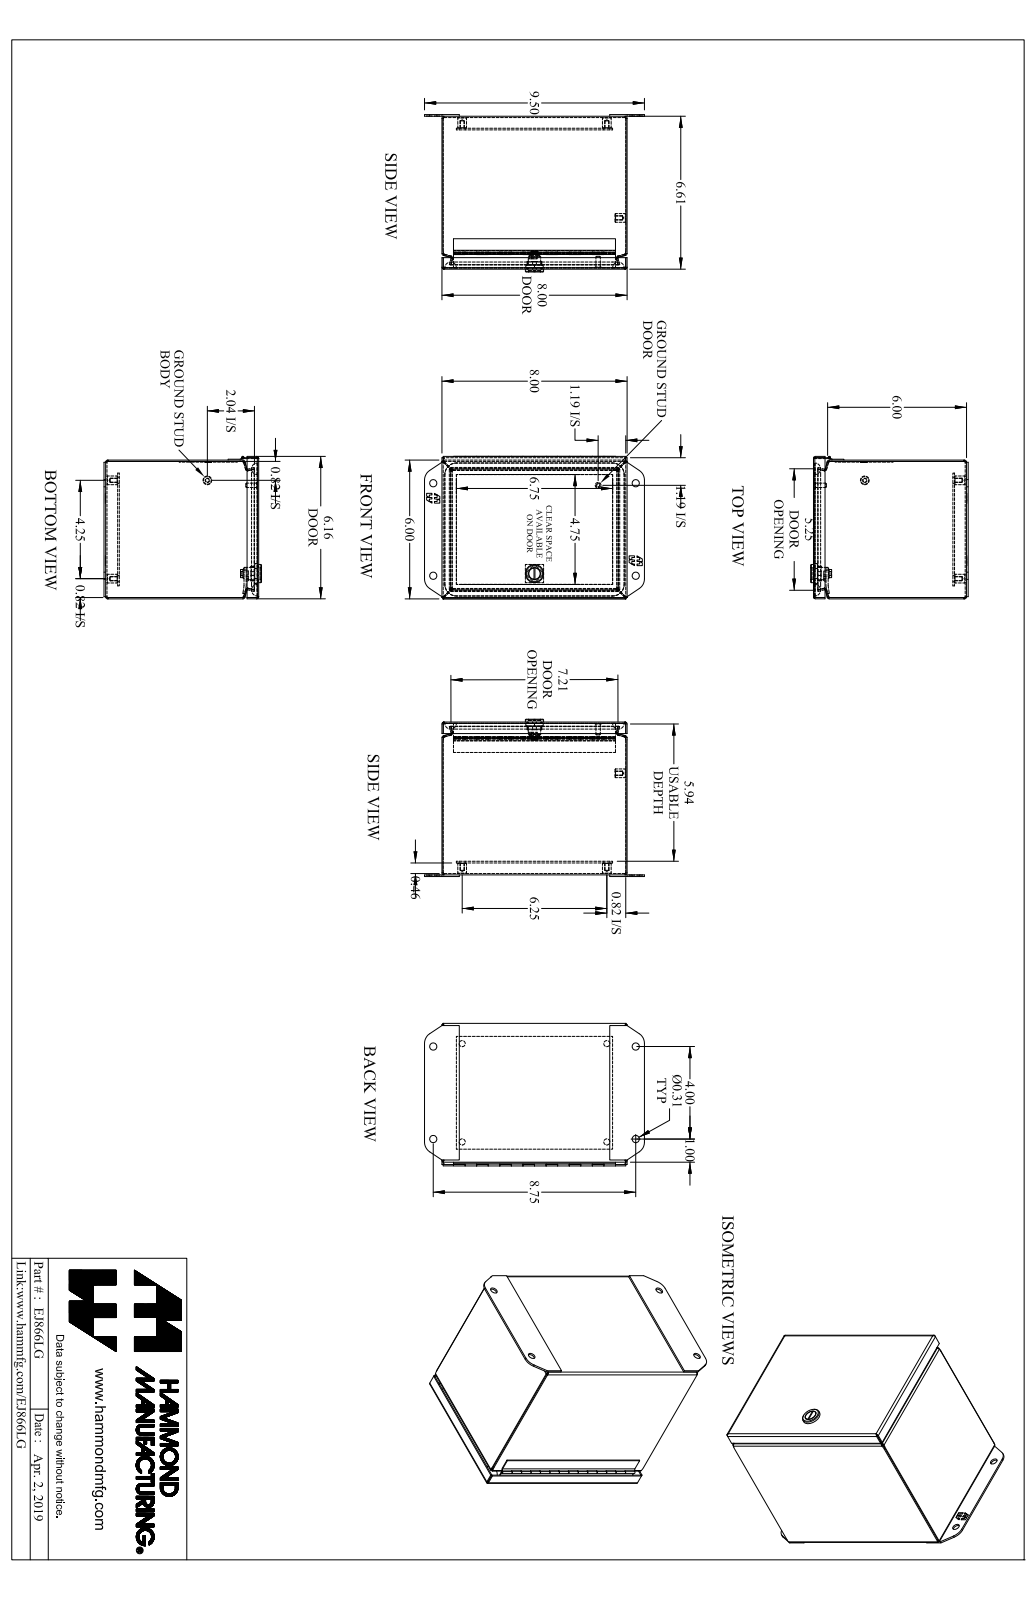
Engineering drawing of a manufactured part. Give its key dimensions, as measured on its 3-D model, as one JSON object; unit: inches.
{"part_name": "EJ866LG_Default", "step_written_by": "SolidWorks 2019 (CONFIG_CONTROL_DESIGN)", "units": "inches", "bodies": {"solids": 16, "faces": 643, "planar": 361, "cylindrical": 190, "other": 92}, "overall_size": [9.5, 6.805, 6.165], "volume_in3": 23.3, "surface_area_in2": 775.7, "round_holes": [[0.156, 5], [0.265, 4], [0.313, 4], [0.05, 1], [0.516, 1]], "round_bosses_or_shafts": [[0.375, 5], [0.788, 1], [0.535, 1], [0.496, 1], [0.435, 1], [0.25, 1], [0.188, 1], [0.1, 1]], "partial_cylinders_radius": [[0.029, 16], [0.086, 16], [0.281, 10], [0.25, 4], [0.499, 4], [0.5, 4], [0.06, 2], [0.539, 2]], "face_to_face_distances": [0.057, 6.554, 5.943, 7.943, 0.072, 0.589, 5.886, 6.611, 6, 6.497], "hole_center_spacings": [1.256, 4.31, 7.502, 8.56, 3.133, 4, 4.25, 4.376]}
